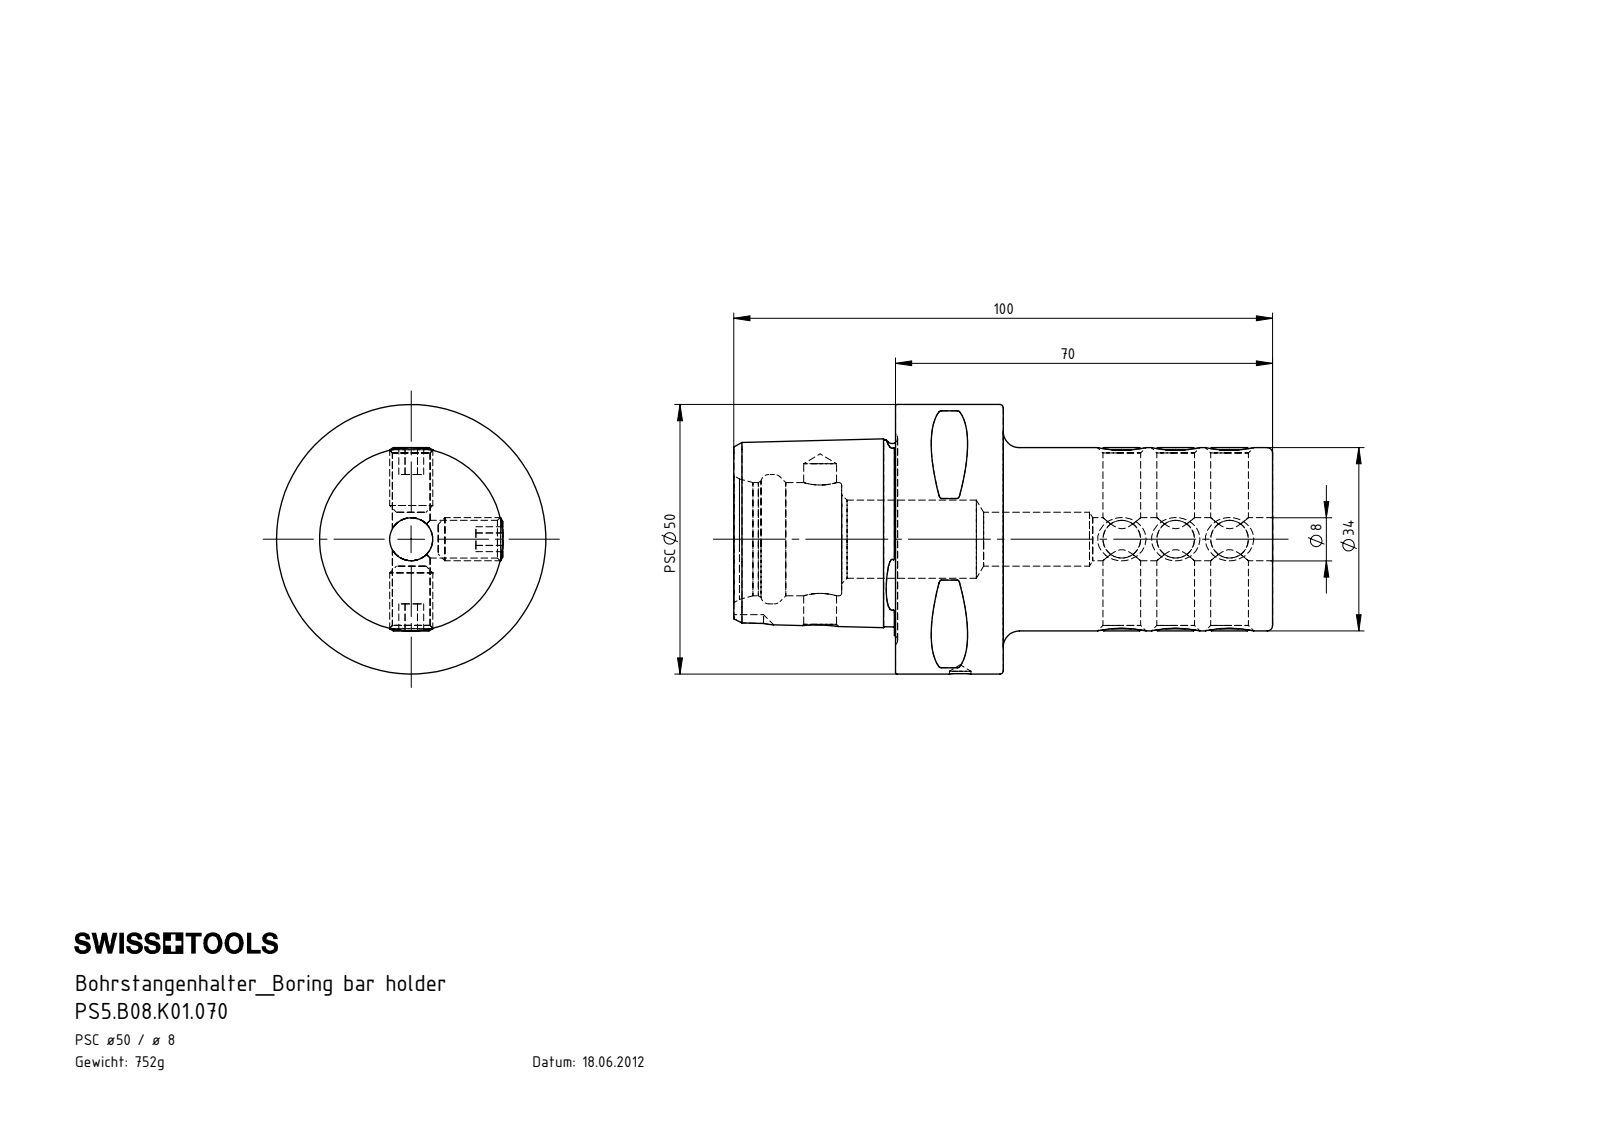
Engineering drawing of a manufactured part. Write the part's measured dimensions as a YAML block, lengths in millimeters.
part_name: "ISO 4026 - M8 x 12_PreviewCfg; PS5.B08.K01.070; PS5-B08.K01.070_A"
step_written_by: "SolidWorks 2017 (AUTOMOTIVE_DESIGN)"
units: millimeters
bodies: {solids: 10, faces: 306, planar: 101, cylindrical: 70, other: 135}
overall_size: [100, 50, 50]
volume: 95817
surface_area: 25347
round_holes:
  - {diameter: 7, count: 6}
  - {diameter: 4, count: 1}
  - {diameter: 6.1, count: 1}
  - {diameter: 8, count: 1}
  - {diameter: 10, count: 1}
  - {diameter: 14.5, count: 1}
  - {diameter: 21, count: 1}
  - {diameter: 24, count: 1}
round_bosses_or_shafts:
  - {diameter: 8, count: 6}
  - {diameter: 50, count: 1}
  - {diameter: 34, count: 1}
partial_cylinders:
  - {radius: 0.5, count: 8}
  - {radius: 4, count: 1}
face_to_face_distances: [50, 20, 70, 30, 10, 5, 100, 4, 12, 19.18]
hole_center_spacings: [10, 20, 26, 30, 40, 50, 56, 66]
